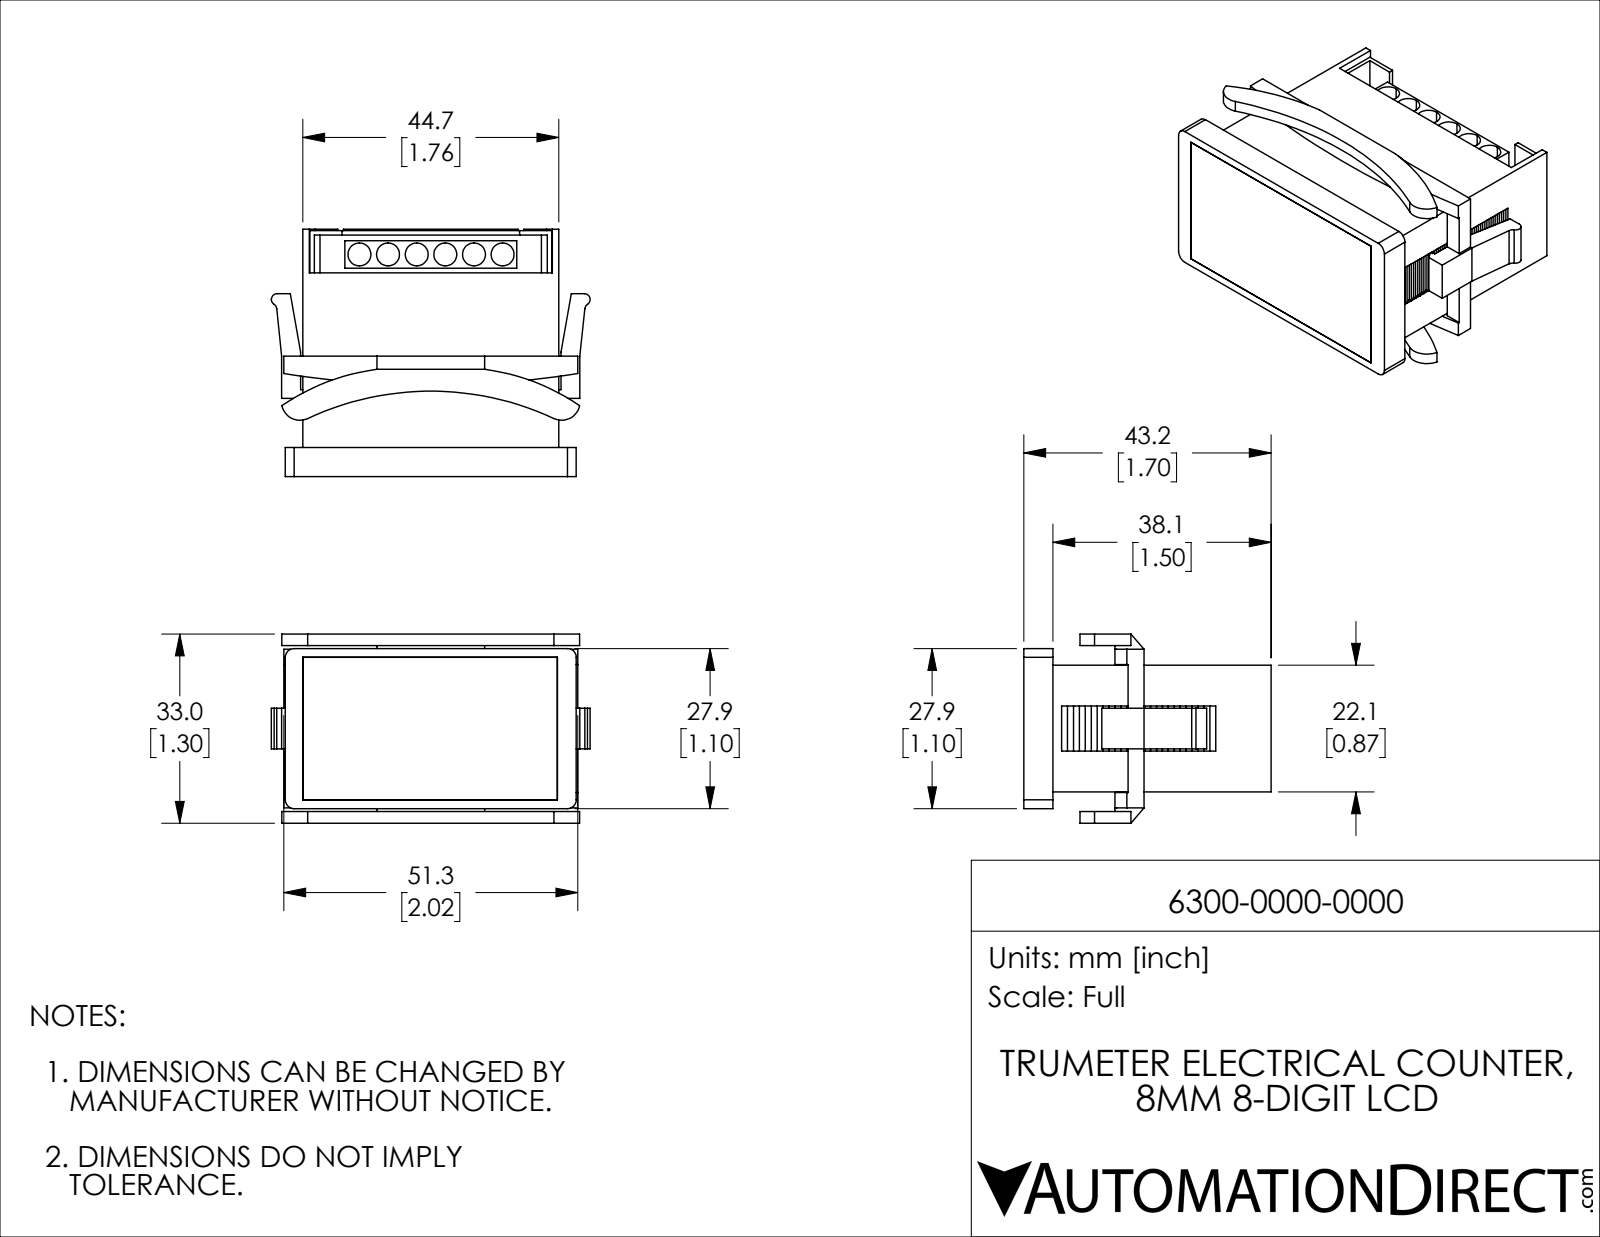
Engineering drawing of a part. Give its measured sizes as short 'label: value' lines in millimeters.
name: 6300-0000-0000
written by: SolidWorks 2021 (CONFIG_CONTROL_DESIGN)
unit: mm
bodies: 6 solids, 464 faces (431 planar, 33 cylindrical, 0 other)
size: 55.66 × 43.18 × 33.02
volume: 22 821 mm³; area: 31 399 mm²
holes: 6× ⌀4
rounds: 4× R1.02, 4× R1.52, 2× R3.2, 2× R38.1, 1× R50.8, 1× R159.51
face distances: 1.14, 2, 20.96, 0.86, 0.76, 1.24, 1.02, 1.52, 22.1, 20.1
hole spacings: 5, 10, 15, 20, 25
